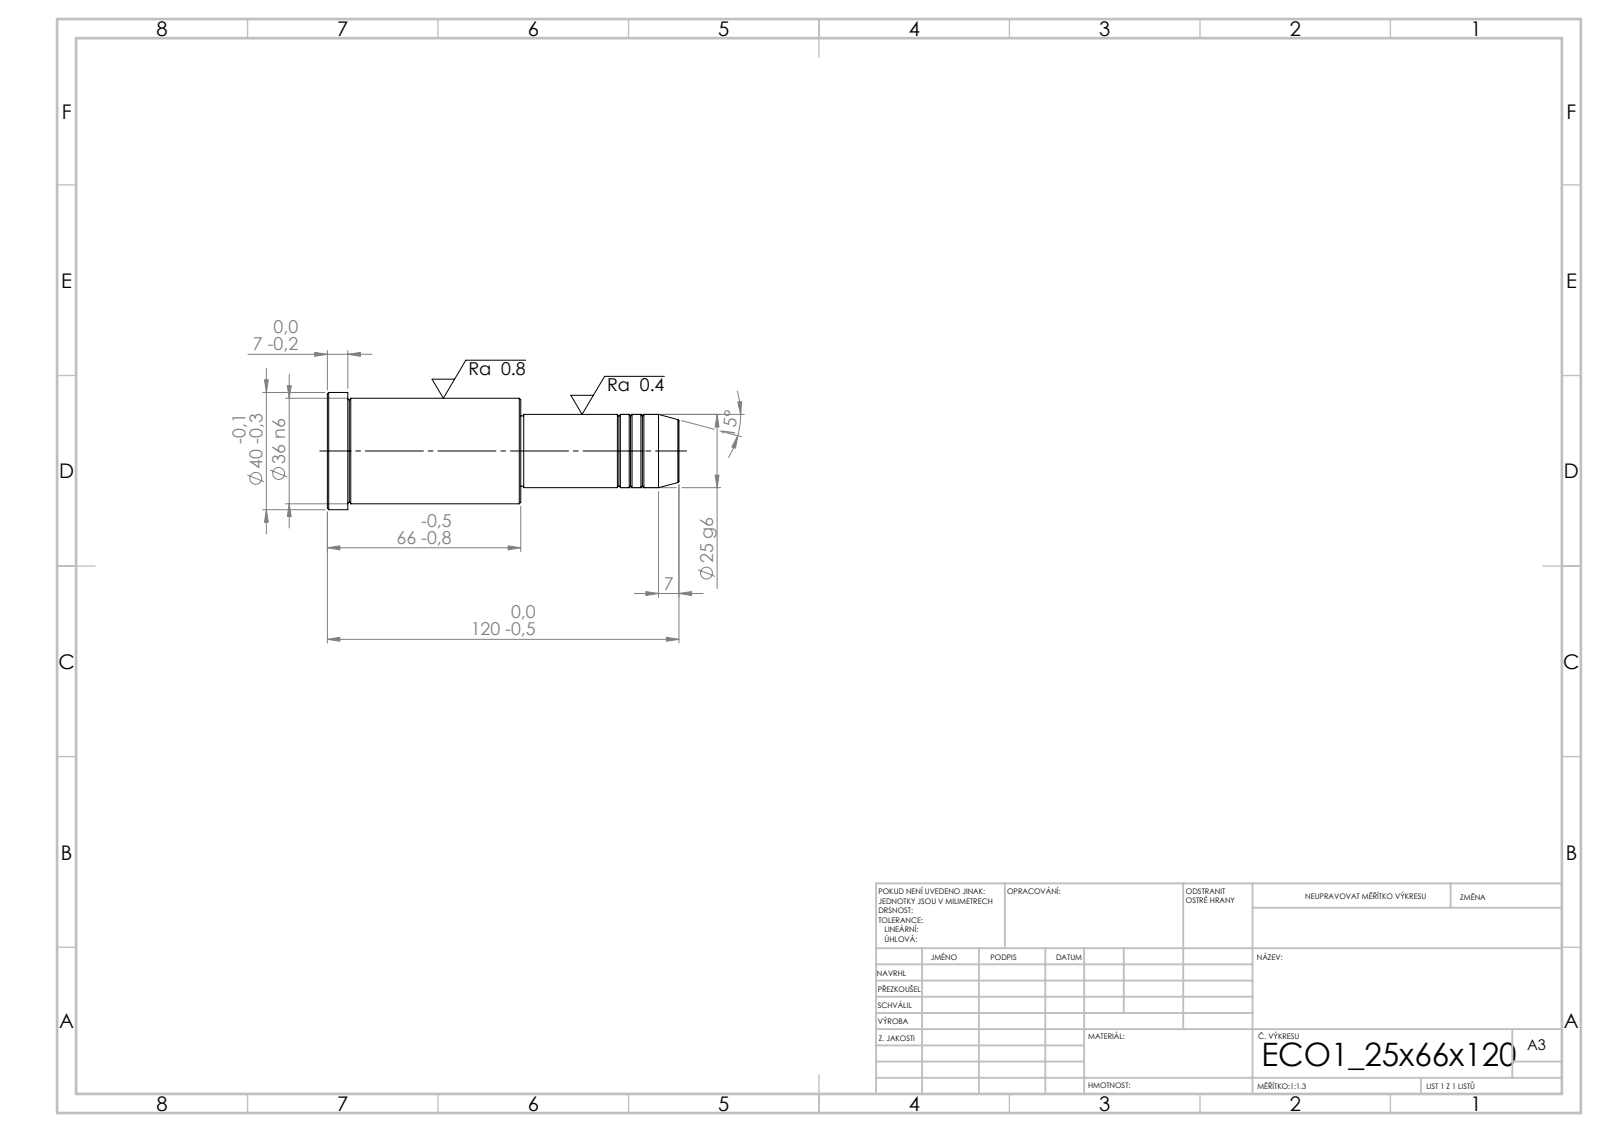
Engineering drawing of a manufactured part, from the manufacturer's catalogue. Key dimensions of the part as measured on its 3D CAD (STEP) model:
STEP written by: SolidWorks 2019 (CONFIG_CONTROL_DESIGN)
Units: millimetres
Bodies: 1 solid, 43 faces (5 planar, 14 cylindrical, 24 other)
Overall size (bounding box): 120 × 40 × 40
Volume: 94 664 mm³ · Surface area: 14 329 mm²
Round bosses / shafts (diameter × count): ⌀40 ×1, ⌀36 ×1, ⌀25 ×1, ⌀24 ×1
Main face-to-face distances: 66, 54, 120, 113, 59, 7, 53, 1, 60, 67
